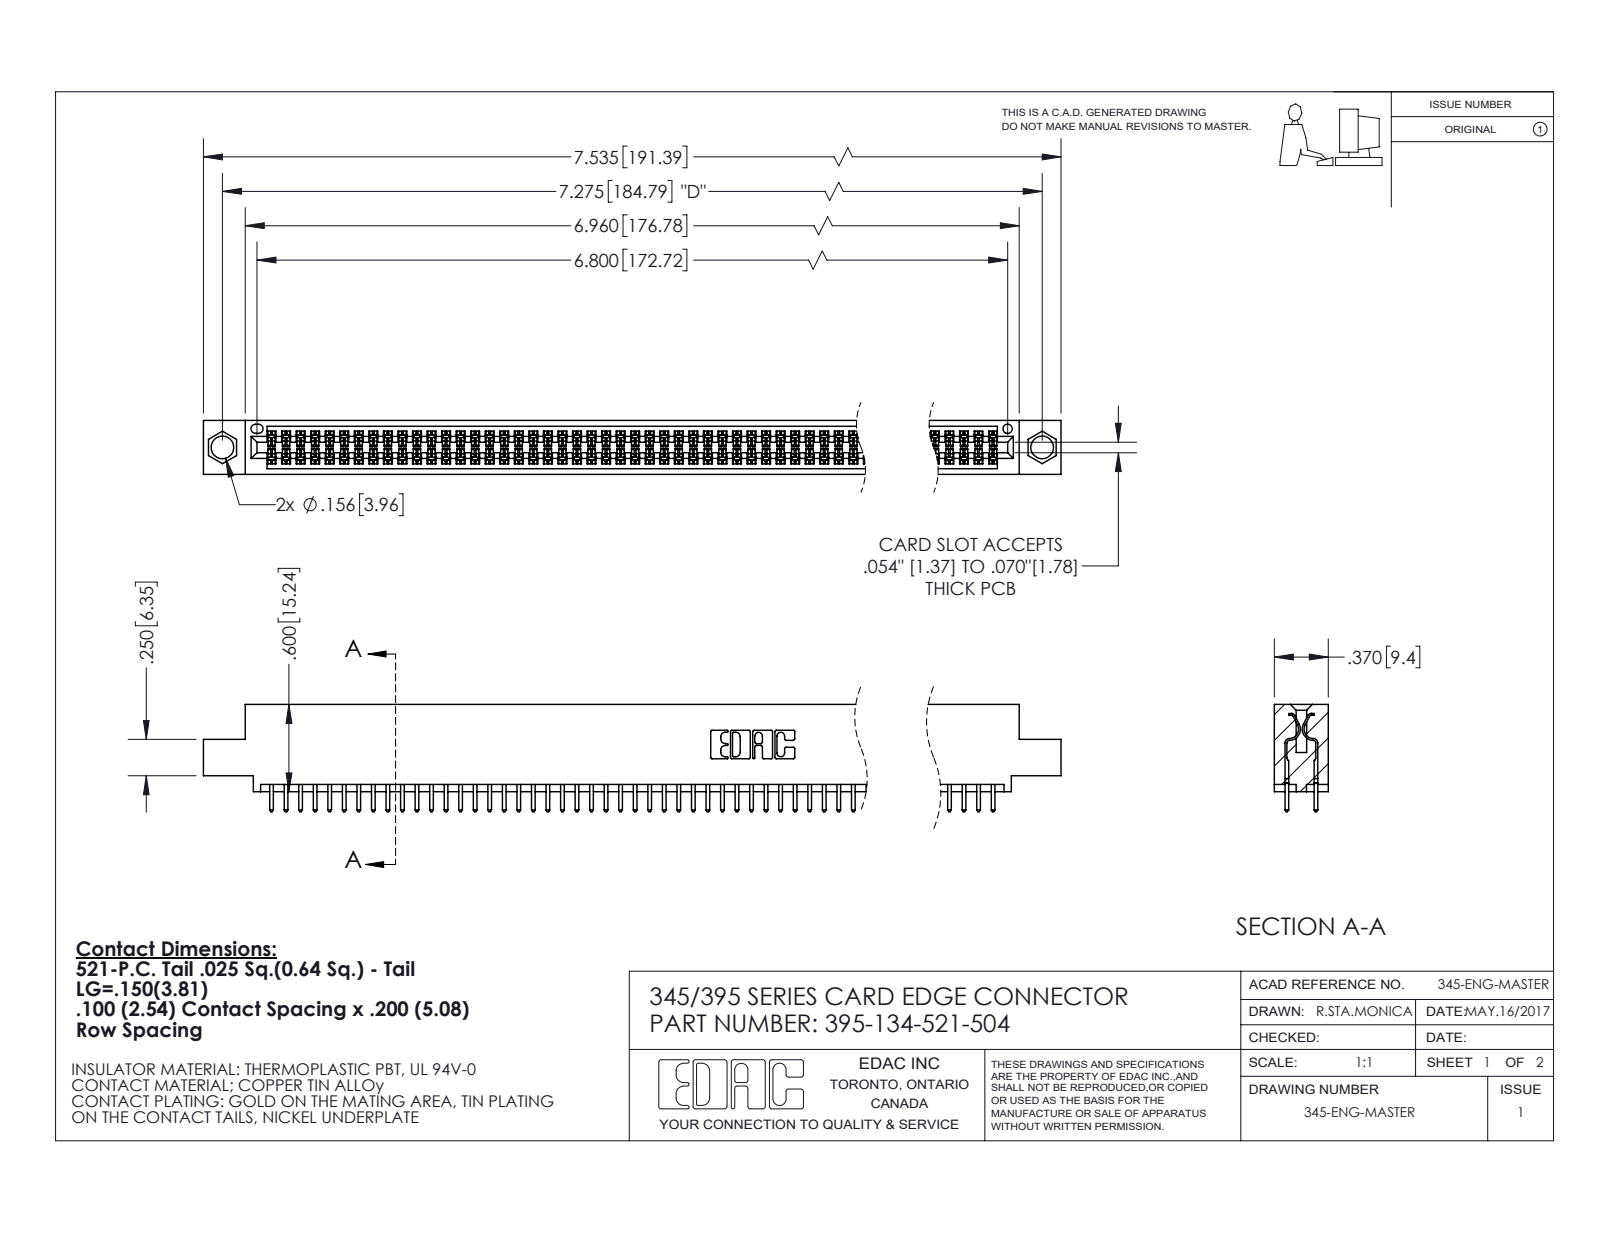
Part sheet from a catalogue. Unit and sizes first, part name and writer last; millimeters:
Units: millimetres
Overall size (bounding box): 191.4 × 18.7 × 9.4
Round holes (diameter × count): ⌀4 ×2, ⌀1.6 ×1
Partial cylindrical surfaces — rounded edges, fillets, slot ends (radius × count): R0.2 ×201, R0.3 ×134, R0.3 ×22, R0.2 ×6, R0.8 ×6, R0.7 ×3, R0.4 ×2, R0.5 ×2
Main face-to-face distances: 1.8, 7.6, 5.1, 2.5, 6.9, 0.6, 9.4, 5.7, 4.4, 3.8
Hole centre spacings: 6.9, 178.8, 184.8
Volume: 18 580 mm³ · Surface area: 27 550 mm²
Bodies: 135 solids, 6844 faces (4520 planar, 2324 cylindrical, 0 other)
Part name (STEP PRODUCT): 345 Part_0.110 Offset - 0.156 Dia-TI; 345-292-001_345-293-121; 395-134-521-504
STEP written by: SolidWorks 2020 (CONFIG_CONTROL_DESIGN)
